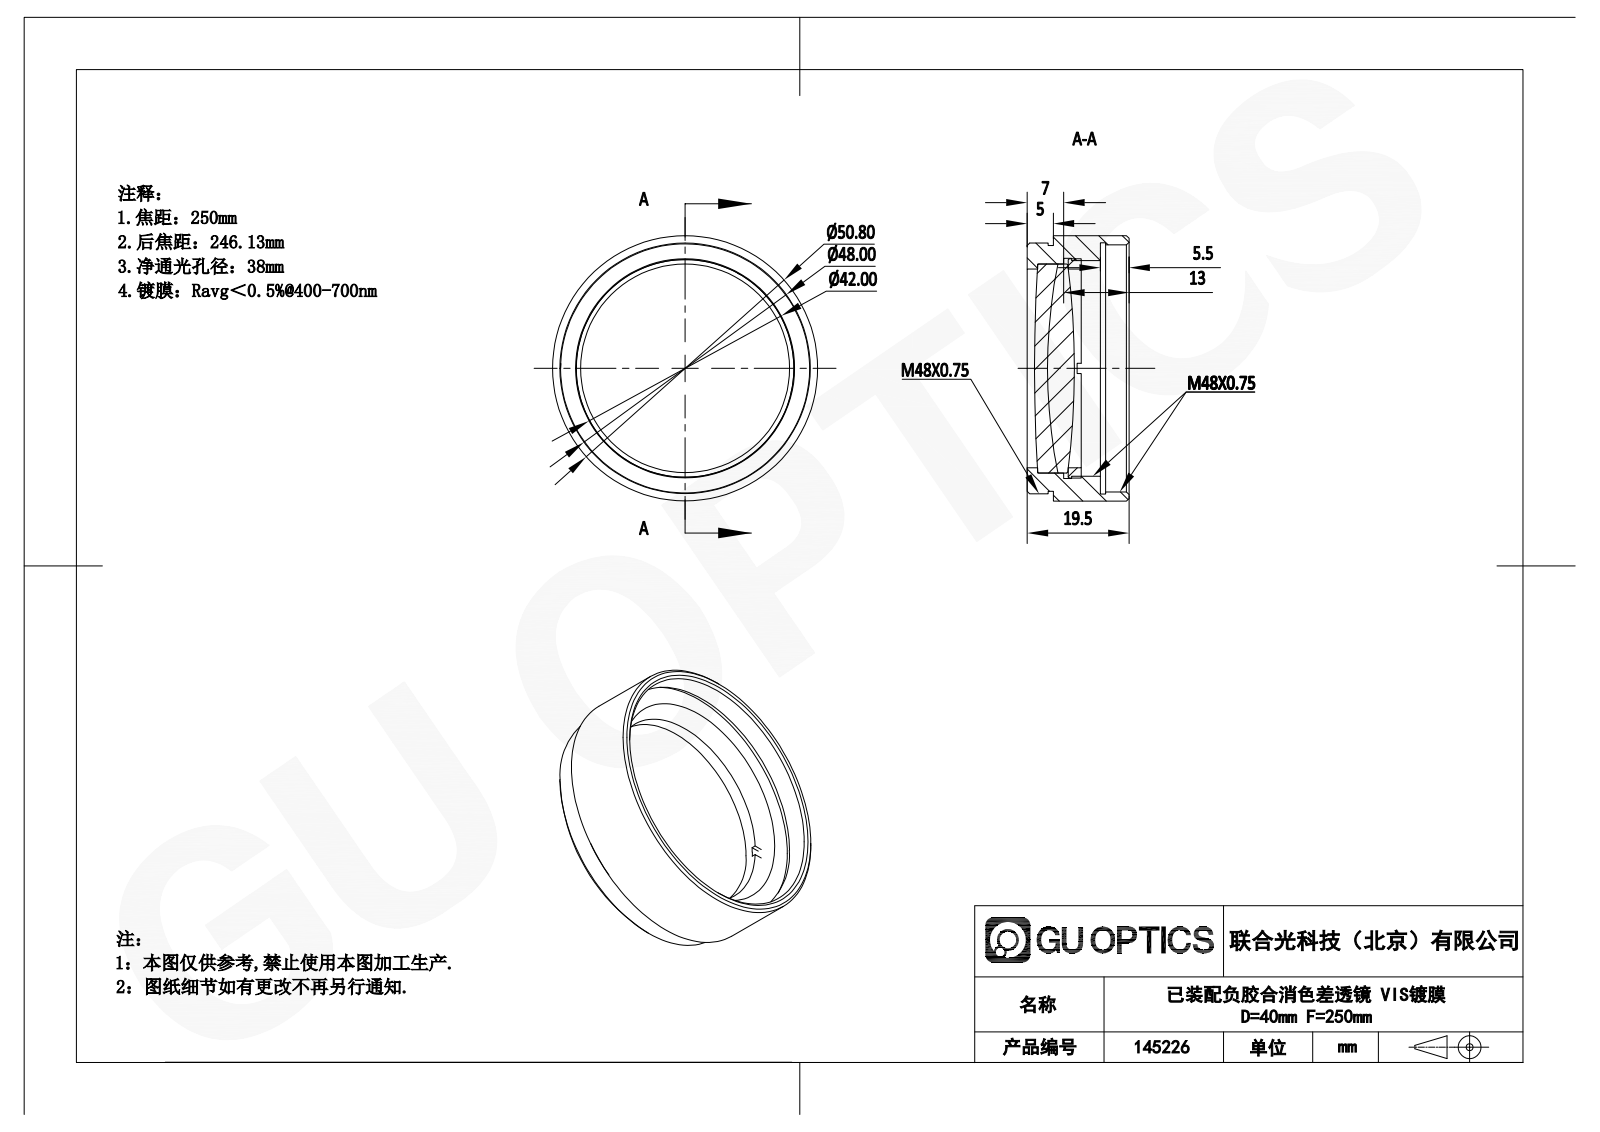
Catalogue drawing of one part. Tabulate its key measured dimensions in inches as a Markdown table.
| quantity | value |
| --- | --- |
| part name | GL31-040-250-VIS_Solidworks; M42x0.75ѹȦ; APD-ML40-250-VIS-A |
| STEP written by | SolidWorks 2022 (AUTOMOTIVE_DESIGN) |
| units | inches |
| bodies | 4 solids, 64 faces (18 planar, 26 cylindrical, 20 other) |
| overall size | 2 × 2 × 0.768 |
| volume | 1.198 in³ |
| surface area | 22.58 in² |
| round holes (diameter × count) | 1.496 × 1, 1.624 × 1, 1.657 × 1, 1.86 × 1, 1.894 × 1 |
| round bosses / shafts (diameter × count) | 2 × 1, 1.89 × 1, 1.85 × 1, 1.654 × 1, 1.575 × 1 |
| main face-to-face distances | 0.551, 0.197, 0.079, 0.354, 0.276, 0.408, 0.211, 0.143, 0.31, 0.113 |
